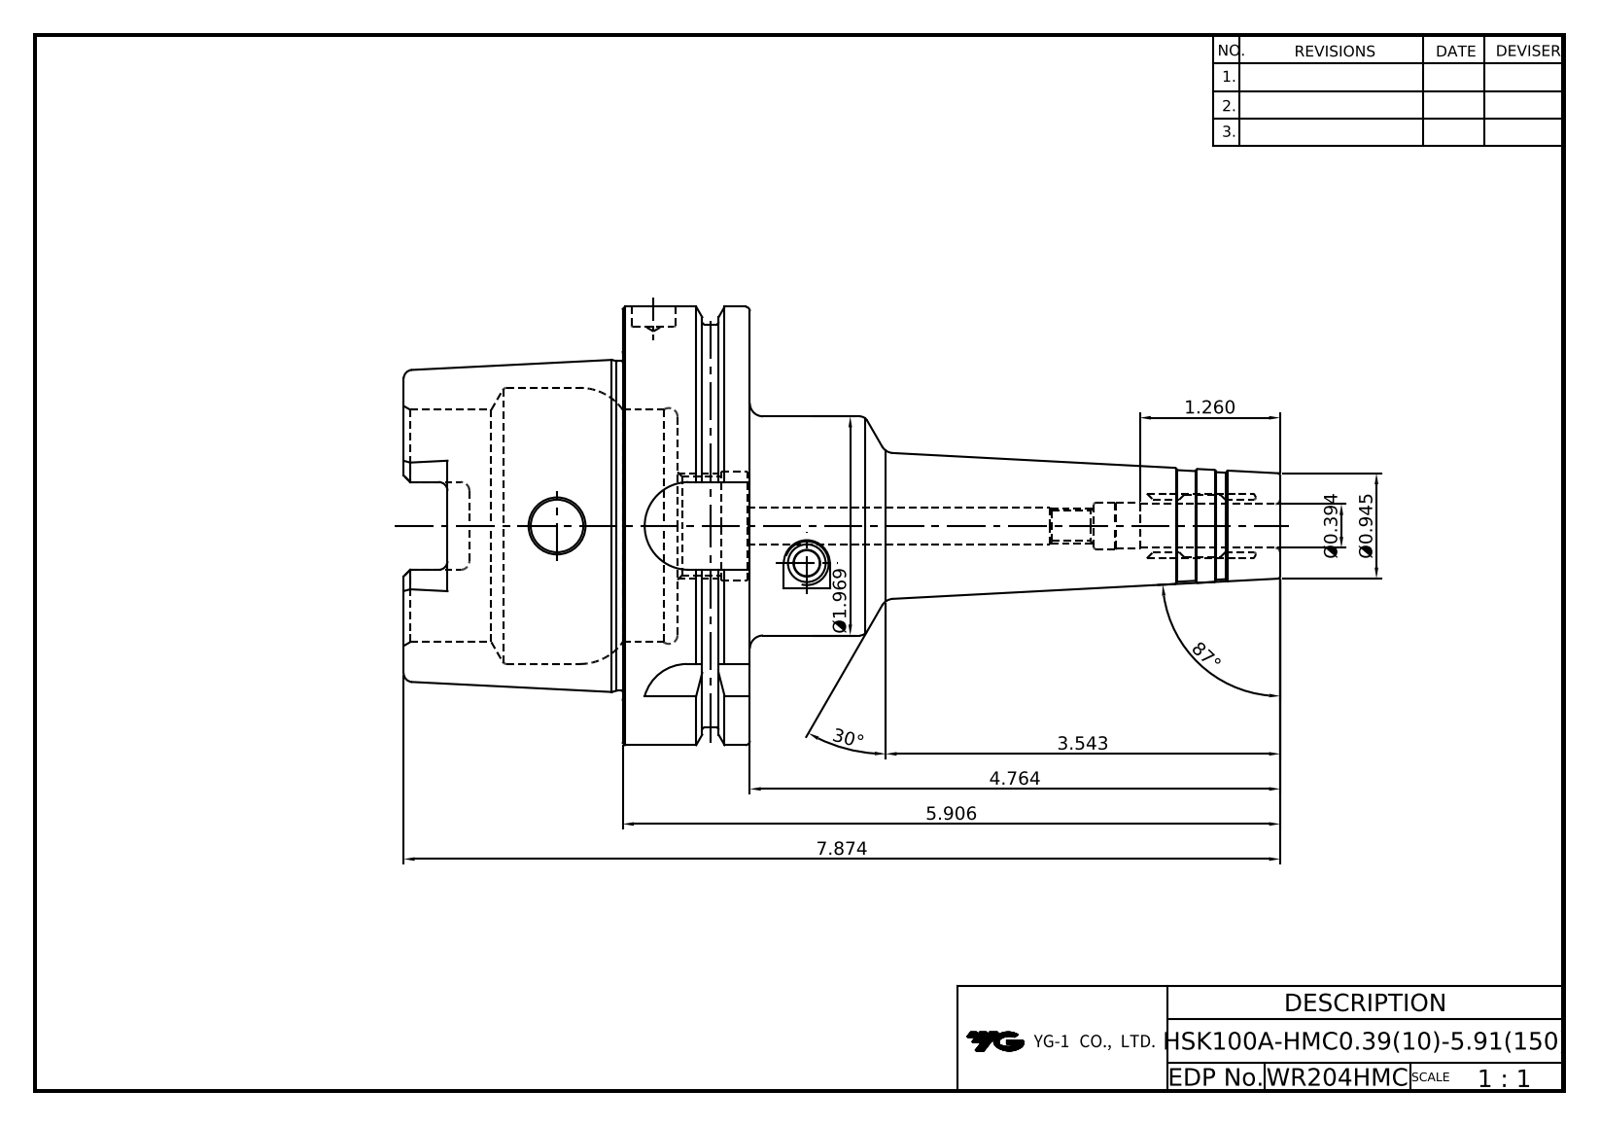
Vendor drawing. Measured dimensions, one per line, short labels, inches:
name: LO-HSK100A-HMC10-150
written by: Autodesk Inventor 2020 (AUTOMOTIVE_DESIGN)
unit: in
bodies: 1 solid, 134 faces (38 planar, 35 cylindrical, 61 other)
size: 7.874 × 3.937 × 3.937
volume: 21.56 in³; area: 99.6 in²
holes: 2× ⌀0.394, 1× ⌀0.272, 1× ⌀0.331, 1× ⌀0.417, 1× ⌀0.472, 1× ⌀0.881, 1× ⌀0.984, 1× ⌀2.087, 1× ⌀2.48
bosses: 1× ⌀3.937, 1× ⌀3.622, 1× ⌀2.969, 1× ⌀1.969
rounds: 6× R0.079, 4× R0.192, 4× R0.394
face distances: 1.142, 0.492, 0.65, 2.461, 3.11, 1.969, 3.091, 3.465, 1.122, 0.63
